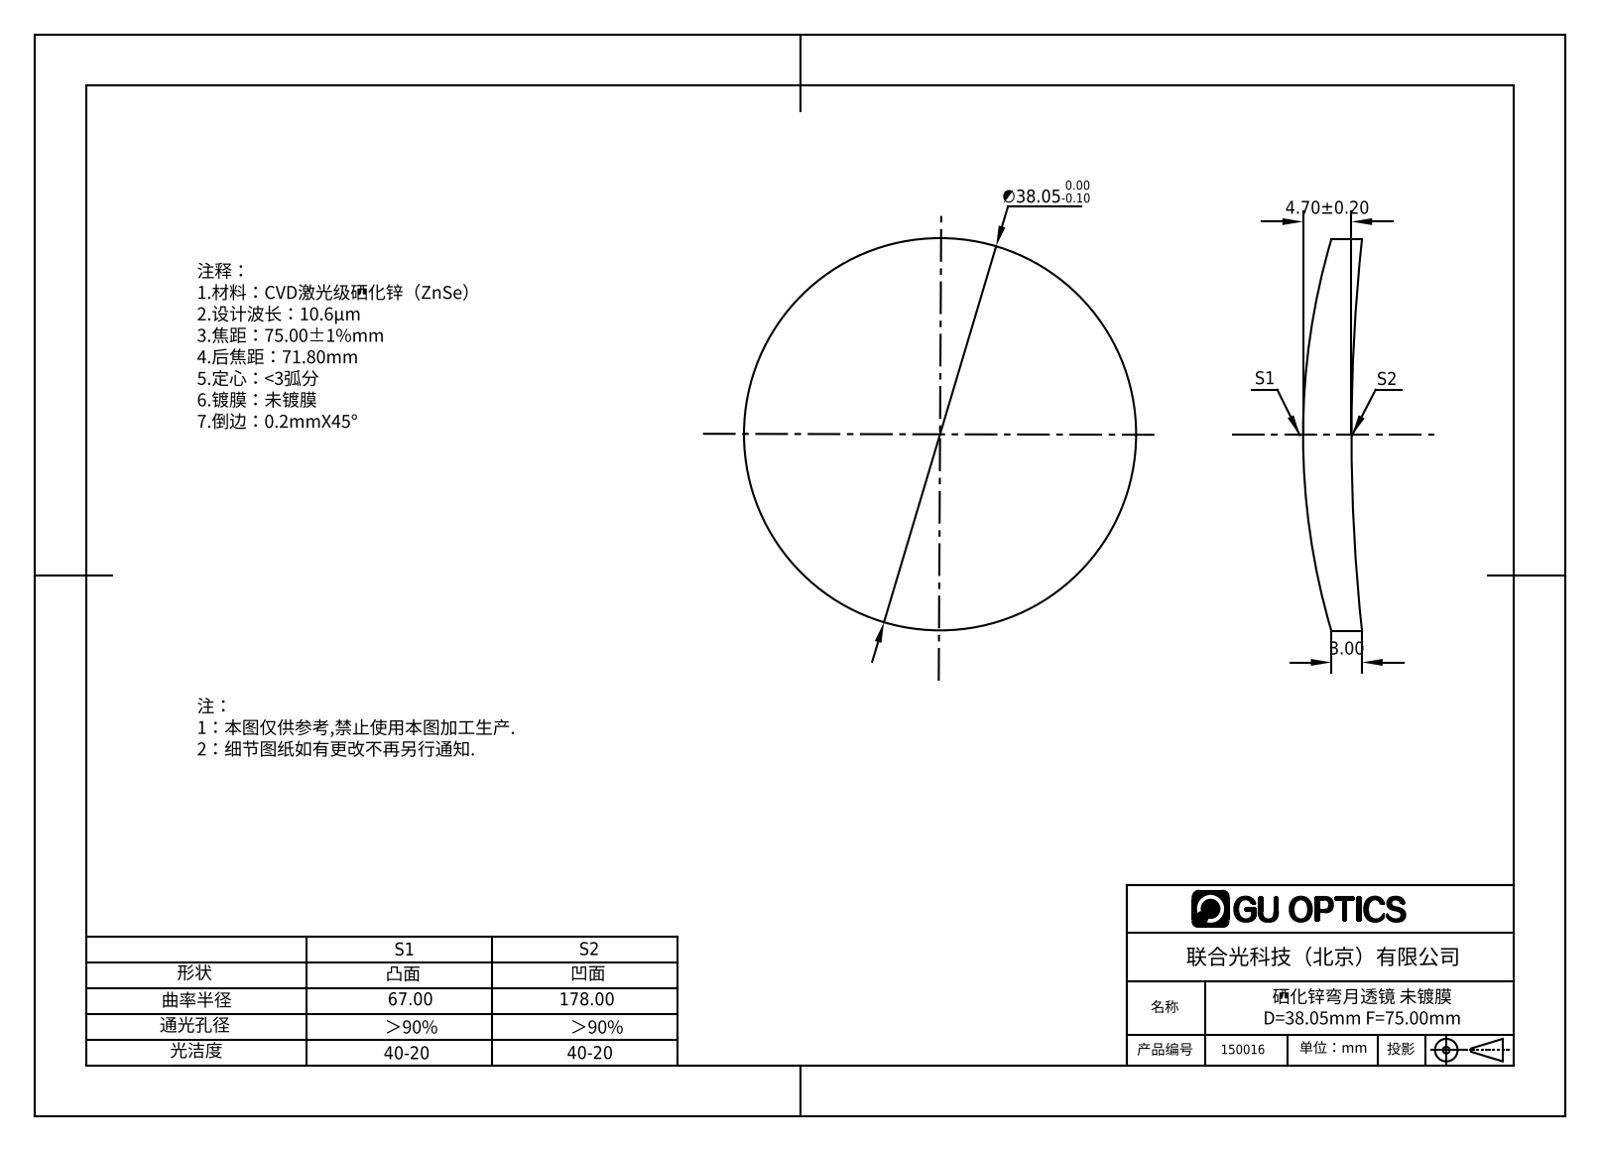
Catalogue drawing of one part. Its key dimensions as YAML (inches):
part_name: "150016"
step_written_by: "SolidWorks 2016 (AUTOMOTIVE_DESIGN)"
units: inches
bodies: {solids: 1, faces: 6, planar: 0, cylindrical: 2, other: 4}
overall_size: [1.498, 1.498, 0.225]
volume: 0.266
surface_area: 4.115
round_bosses_or_shafts:
  - {diameter: 1.498, count: 1}
